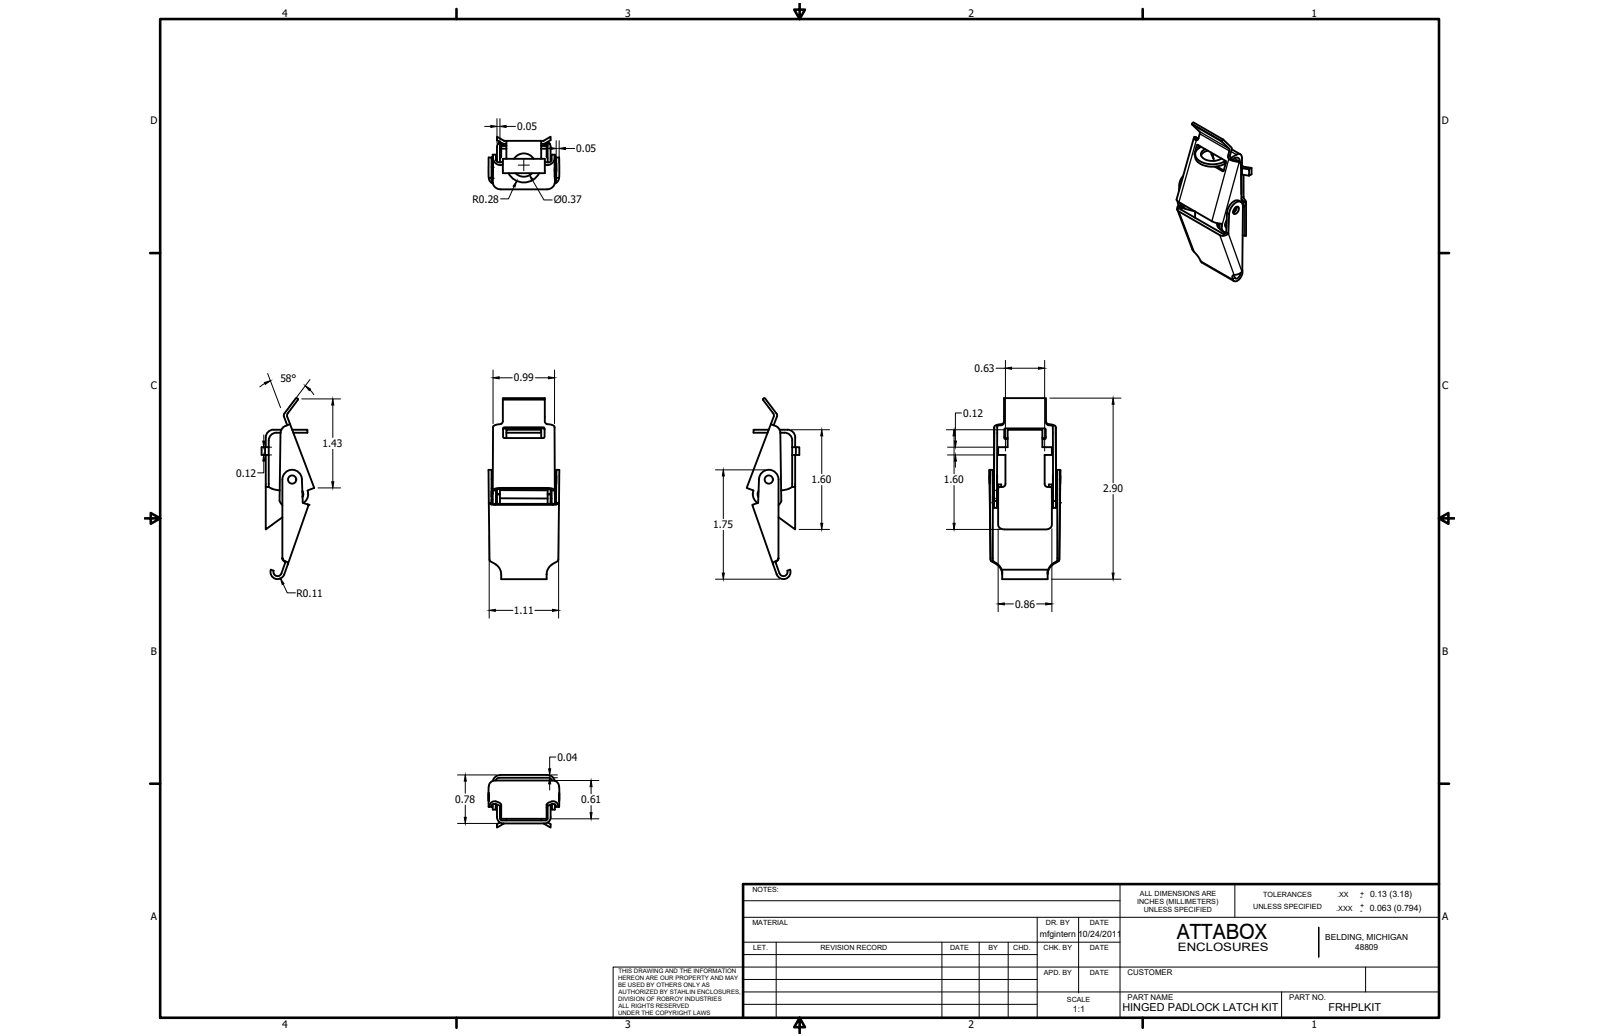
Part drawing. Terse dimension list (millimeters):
name: FRHPLKIT
written by: SolidWorks 2019 (AUTOMOTIVE_DESIGN)
unit: mm
bodies: 5 solids, 158 faces (83 planar, 68 cylindrical, 7 other)
size: 74.2 × 30.5 × 23.4
volume: 5 460 mm³; area: 9 310 mm²
holes: 2× ⌀3.4, 2× ⌀3.4, 1× ⌀9.5
bosses: 1× ⌀7.6, 1× ⌀4.2, 1× ⌀3.8, 1× ⌀3.2
rounds: 11× R1.5, 8× R0.8, 6× R1.1, 4× R0.4, 3× R4, 2× R0.6, 2× R2.4, 2× R4.7
face distances: 1.3, 23.9, 1.3, 25.4, 1.5, 1.3, 25.2, 26.7, 23.4, 22.1
hole spacings: 6.5
